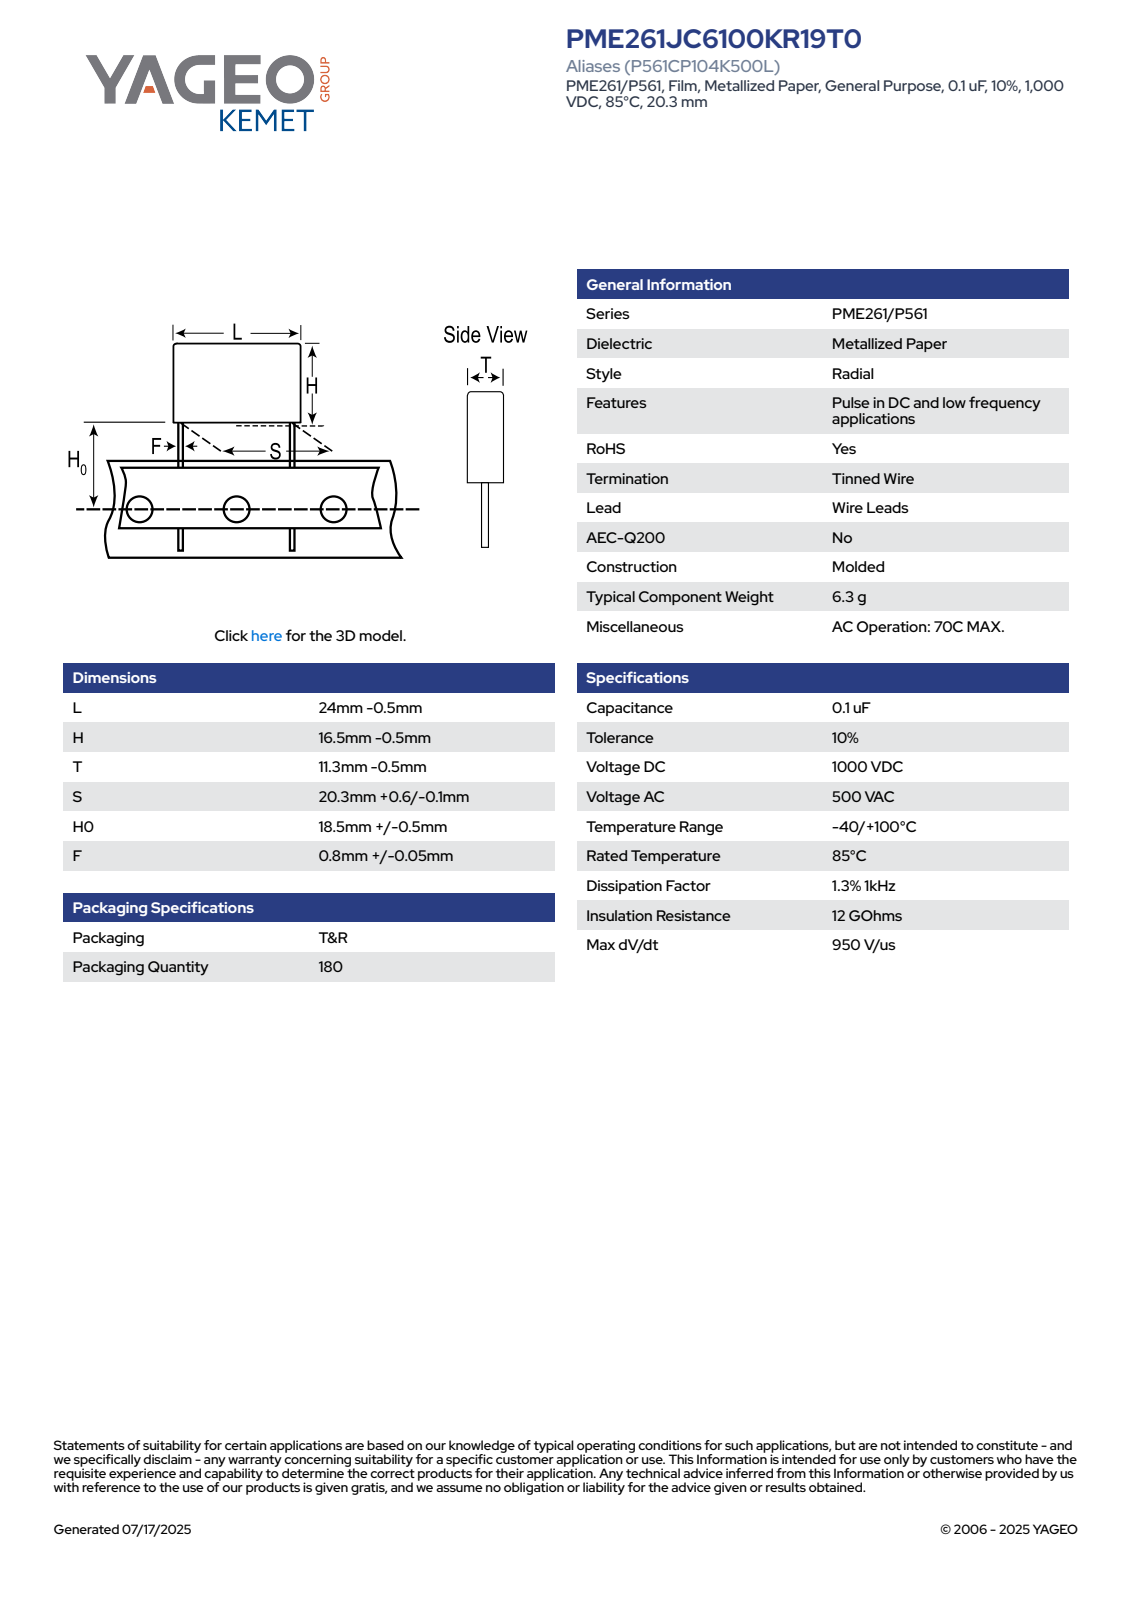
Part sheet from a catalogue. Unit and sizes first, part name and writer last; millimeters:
Units: millimetres
Overall size (bounding box): 35 × 23.5 × 10.8
Round bosses / shafts (diameter × count): ⌀0.85 ×2
Partial cylindrical surfaces — rounded edges, fillets, slot ends (radius × count): R0.5 ×4
Main face-to-face distances: 10.8, 16, 23.5, 19, 35, 27.81, 8.81, 7.19, 25.71, 6.71
Volume: 4 079 mm³ · Surface area: 1 718 mm²
Bodies: 4 solids, 73 faces (65 planar, 8 cylindrical, 0 other)
Part name (STEP PRODUCT): CFR_MOLDED_24X16.5X11.3_L23.5H16T10.8S20.3H019F0.85
STEP written by: SolidWorks 2014 (AUTOMOTIVE_DESIGN)
